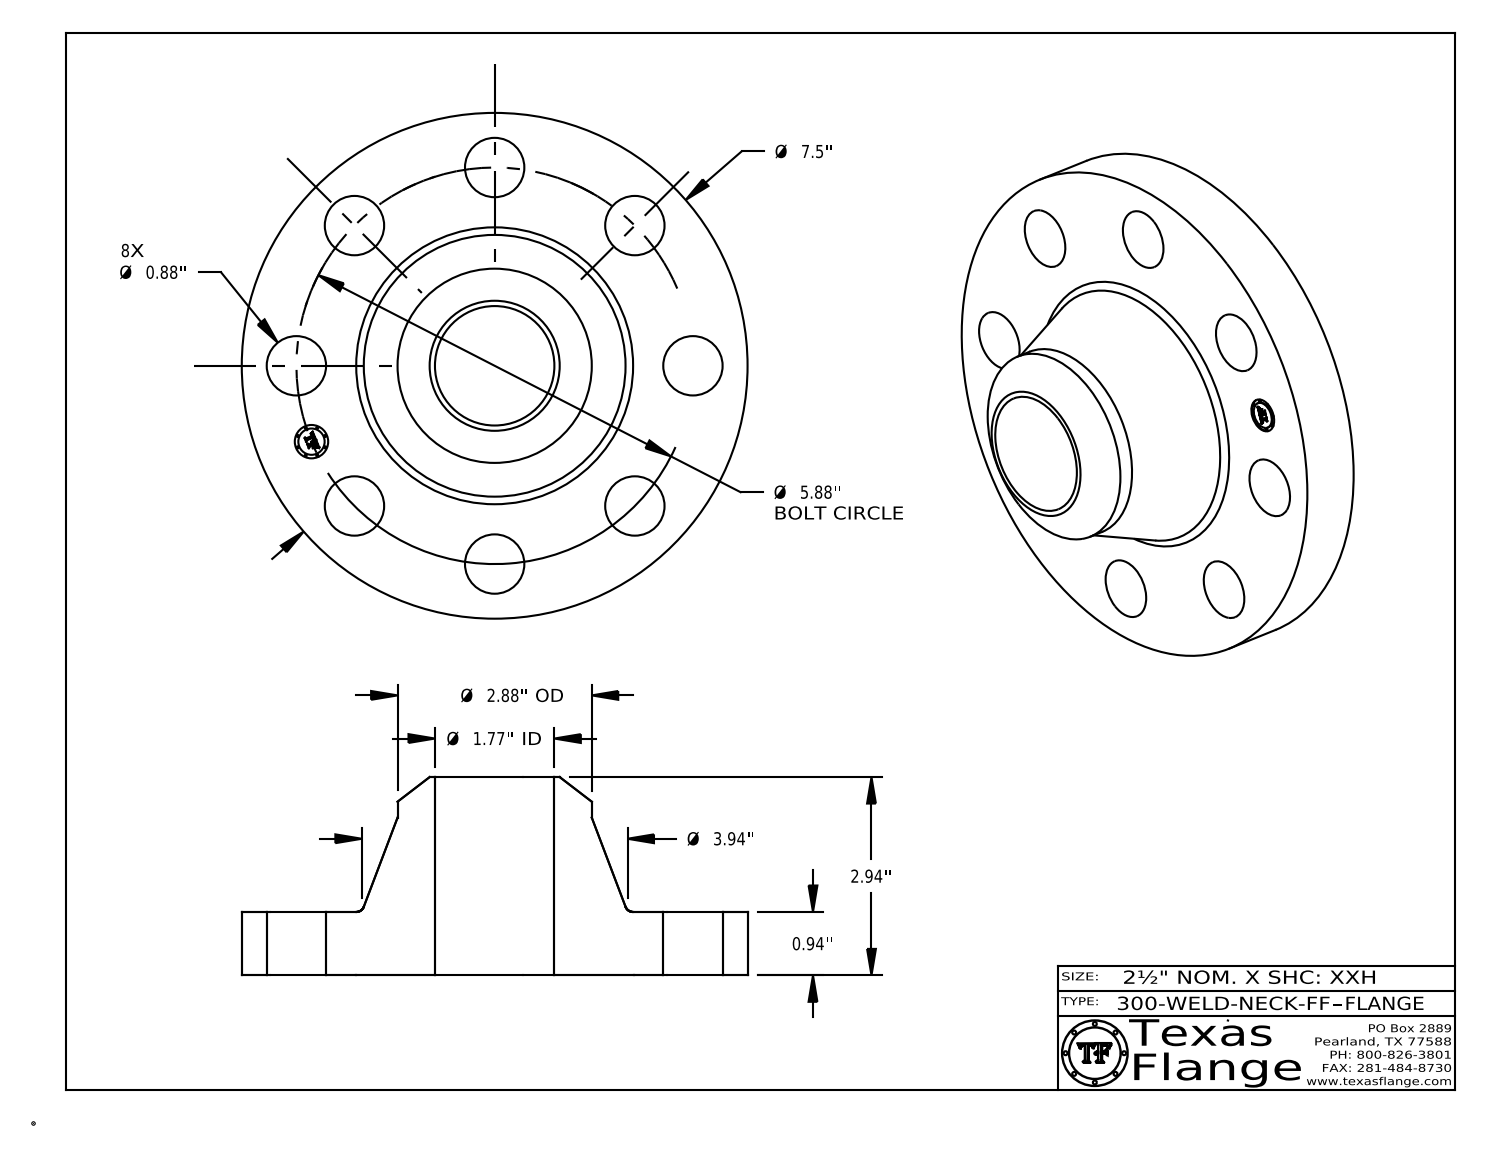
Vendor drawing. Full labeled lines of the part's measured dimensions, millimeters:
Part name (STEP PRODUCT): 300-WELD-NECK-FF
STEP written by: CATIA V5 STEP AP214 (AUTOMOTIVE_DESIGN)
Units: millimetres
Bodies: 1 solid, 417 faces (369 planar, 42 cylindrical, 6 other)
Overall size (bounding box): 190.5 × 190.5 × 74.7
Volume: 750 900 mm³ · Surface area: 94 390 mm²
Round holes (diameter × count): ⌀22.4 ×8, ⌀12.6 ×1, ⌀45 ×1
Round bosses / shafts (diameter × count): ⌀0.8 ×8, ⌀190.5 ×1, ⌀73.2 ×1, ⌀9.9 ×1
Main face-to-face distances: 23.9, 74.7, 50.8, 0.4, 23.5, 51.2, 3.8, 3.7, 0.7, 2.4
Hole centre spacings: 57.2, 138, 74.7, 74.7, 105.6, 105.6, 83, 149.4
